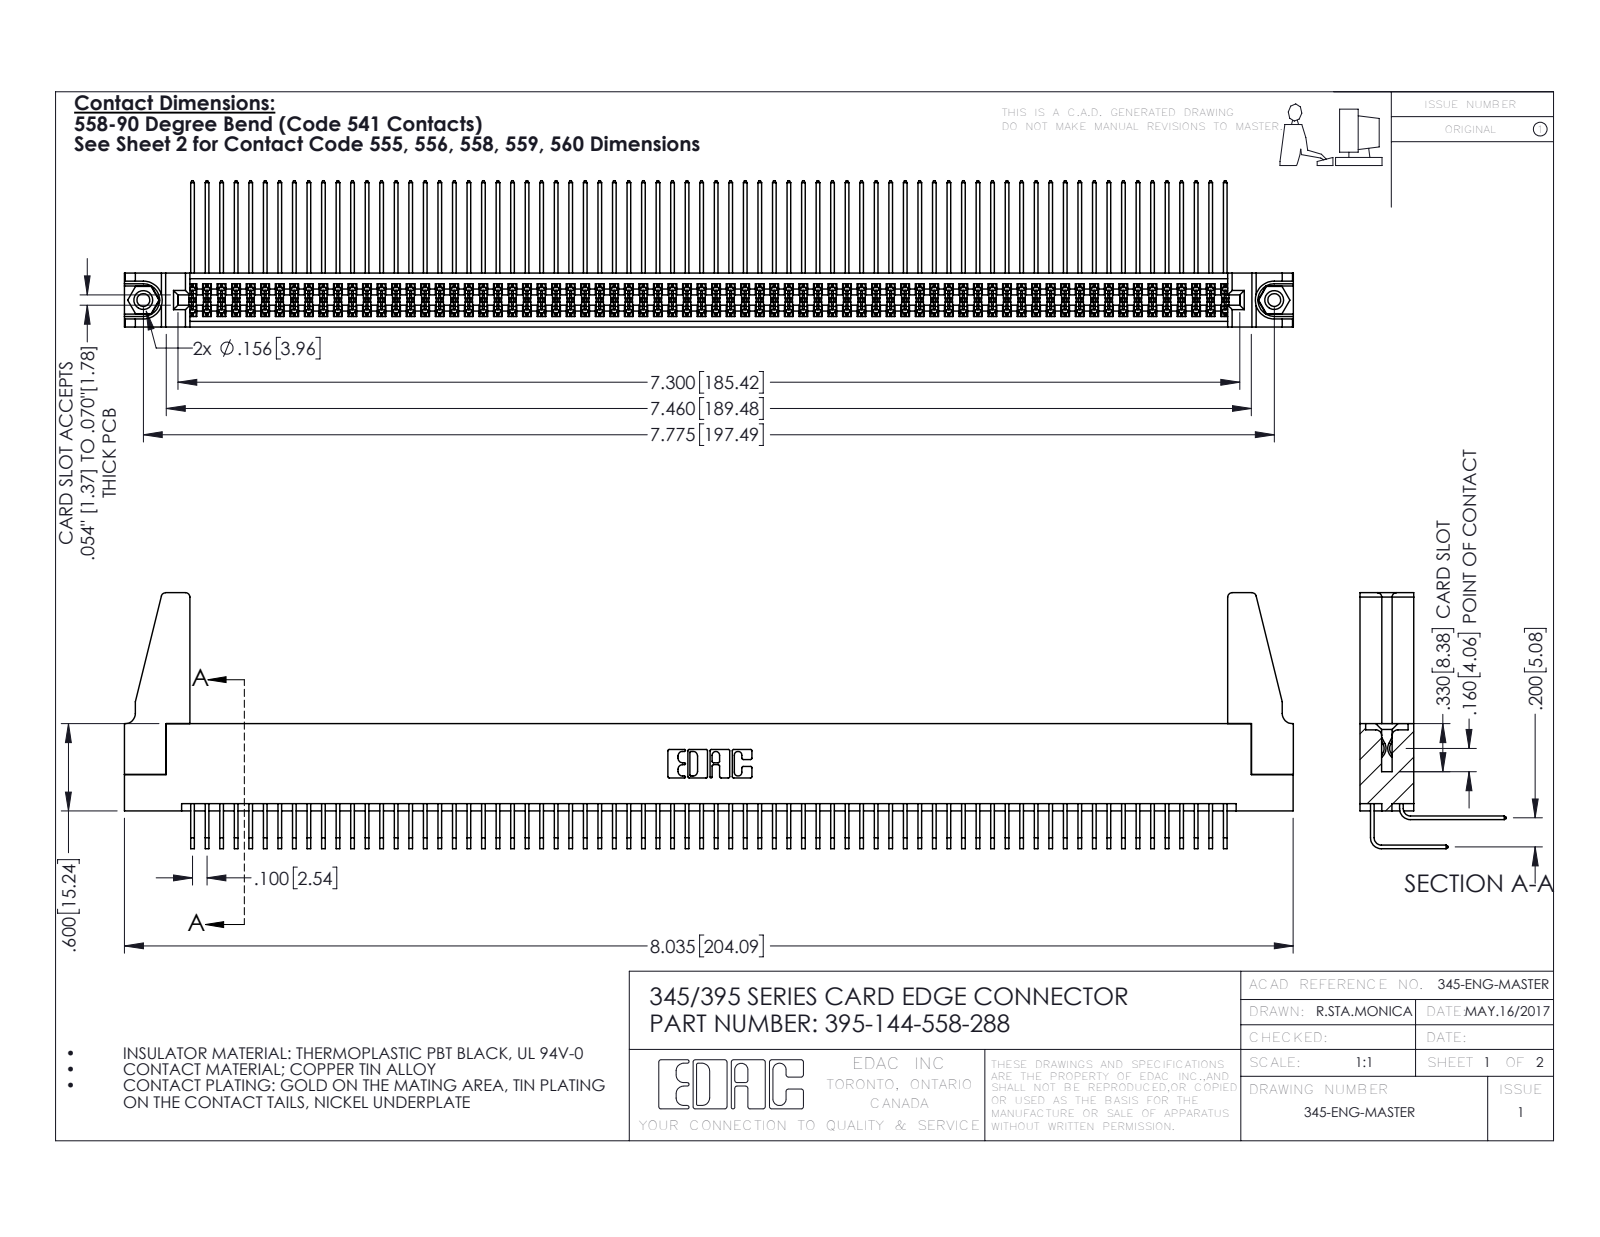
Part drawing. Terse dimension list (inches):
name: 345-220-078_345-220-088; 395-144-558-288; 345-292-001_558 Tail - 2; 345-292-001_558 559 Tail - 1 (+2 more)
written by: SolidWorks 2016 (CONFIG_CONTROL_DESIGN)
unit: in
bodies: 149 solids, 7738 faces (5192 planar, 2530 cylindrical, 16 other)
size: 8.036 × 1.759 × 1.005
volume: 1.476 in³; area: 59.76 in²
holes: 2× ⌀0.089, 2× ⌀0.125, 2× ⌀0.156, 1× ⌀0.064
bosses: 2× ⌀0.155
rounds: 216× R0.006, 22× R0.01, 8× R0.03, 6× R0.007, 6× R0.031, 3× R0.026, 2× R0.014, 2× R0.019
face distances: 0.072, 0.298, 0.2, 0.37, 0.098, 0.272, 0.025, 0.225, 0.025, 0.175
hole spacings: 0.27, 7.539, 7.775
